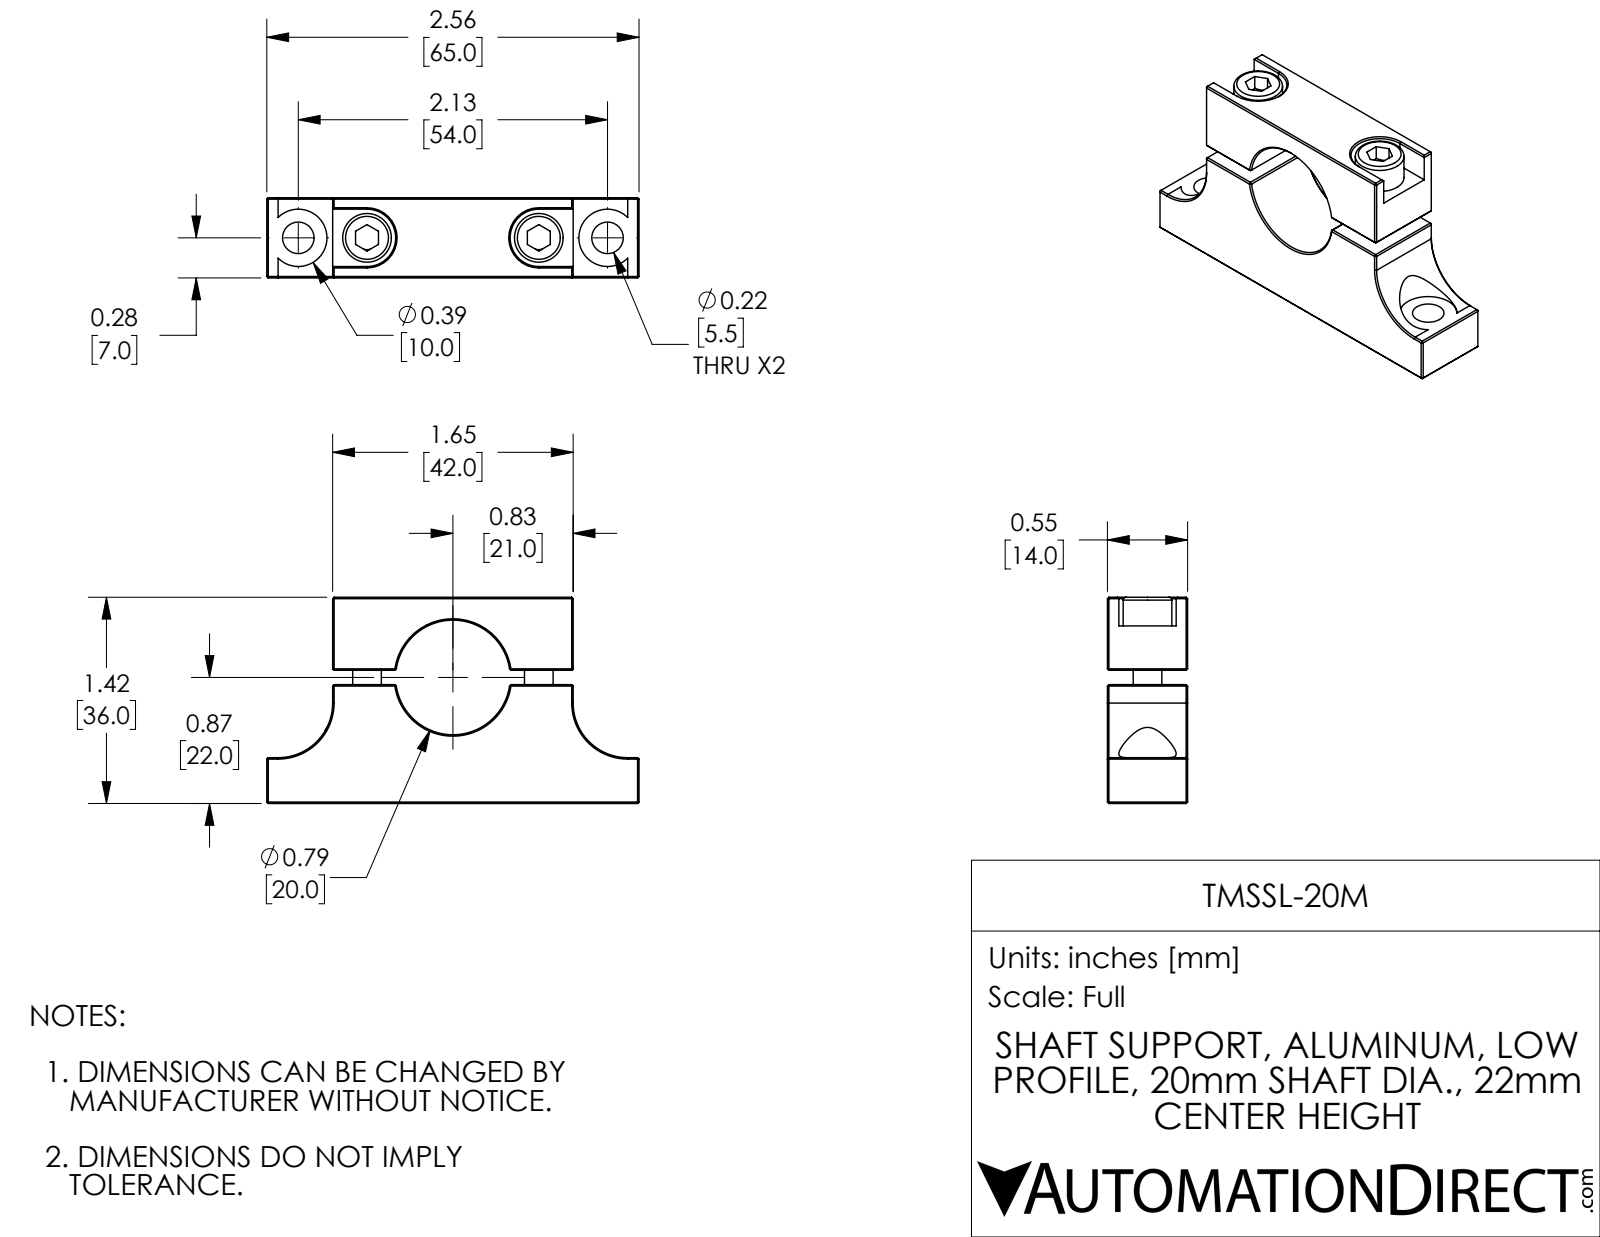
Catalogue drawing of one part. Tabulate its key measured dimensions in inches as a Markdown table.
| quantity | value |
| --- | --- |
| part name | TMSSL-20M |
| STEP written by | SolidWorks 2017 (AUTOMOTIVE_DESIGN) |
| units | inches |
| bodies | 4 solids, 179 faces (118 planar, 32 cylindrical, 29 other) |
| overall size | 2.559 × 1.417 × 0.551 |
| volume | 1.08 in³ |
| surface area | 13.7 in² |
| round holes (diameter × count) | 0.217 × 4, 0.163 × 2, 0.094 × 1, 0.787 × 1 |
| round bosses / shafts (diameter × count) | 0.335 × 2, 0.197 × 2 |
| partial cylindrical surfaces (radius × count) | 0.197 × 4, 0.375 × 2 |
| main face-to-face distances | 0.551, 1.417, 0.6, 0.502, 0.817, 0.915, 0.098, 1.22, 0.404, 0.305 |
| hole center spacings | 0.472, 0.591, 1.063, 1.654, 1.181, 2.126 |
